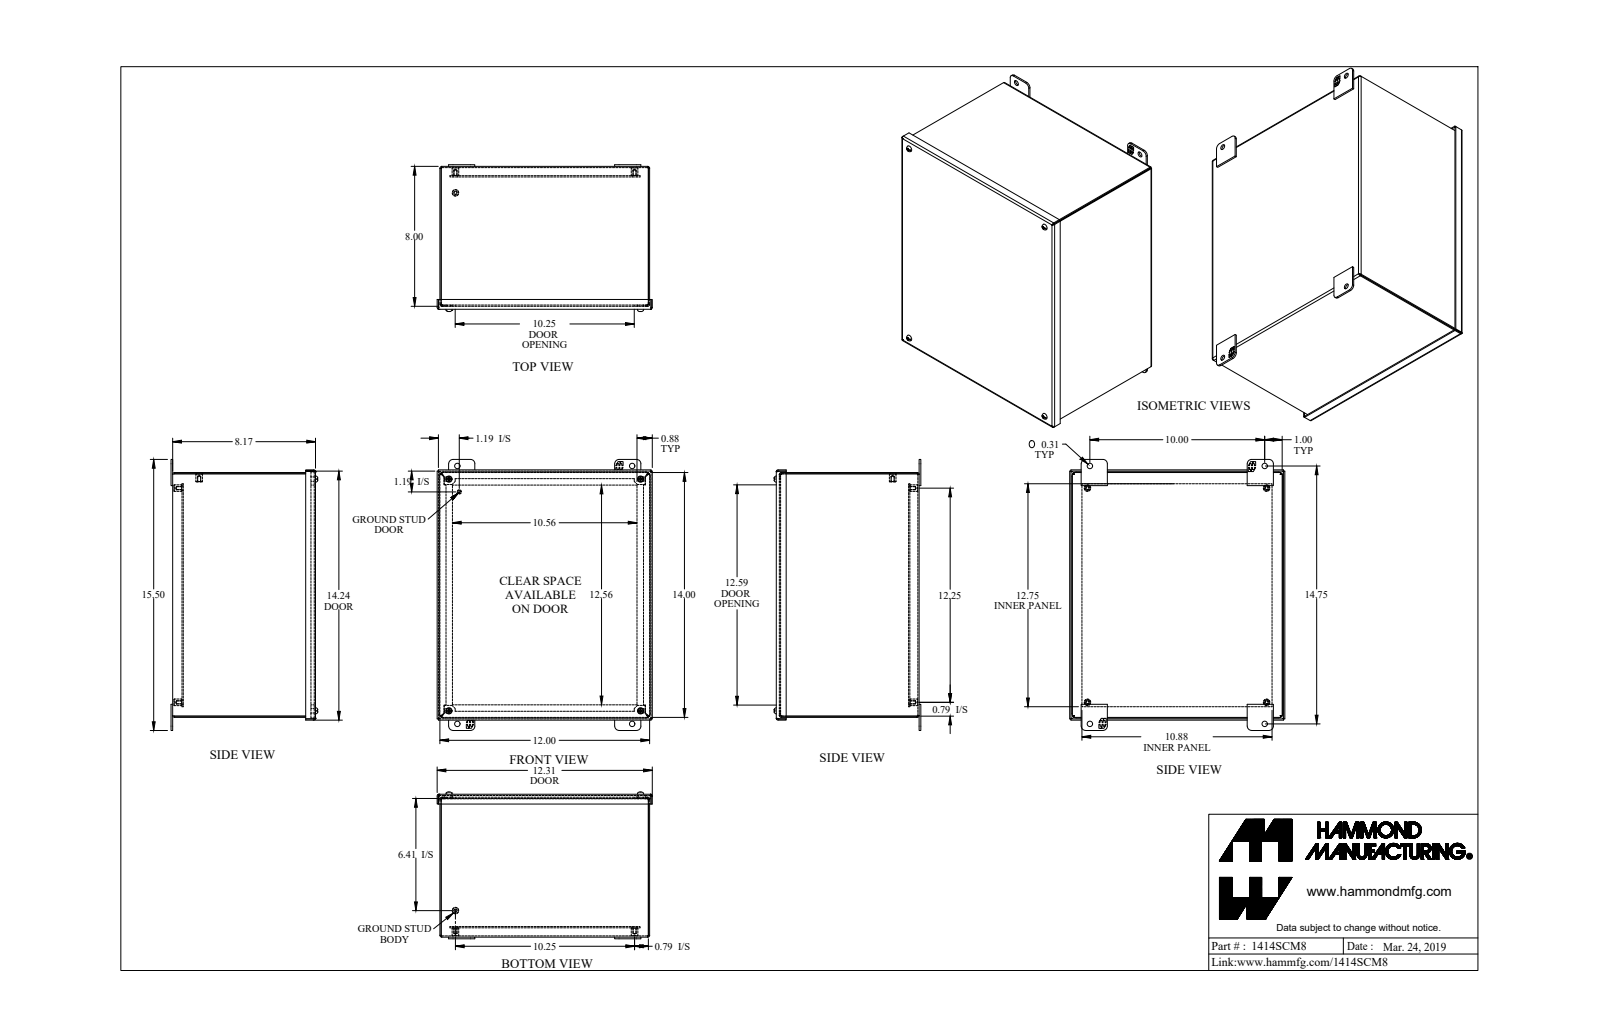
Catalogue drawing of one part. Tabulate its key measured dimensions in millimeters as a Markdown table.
| quantity | value |
| --- | --- |
| part name | 1414SCM8 |
| STEP written by | SolidWorks 2019 (AUTOMOTIVE_DESIGN) |
| units | millimeters |
| bodies | 30 solids, 710 faces (478 planar, 172 cylindrical, 60 other) |
| overall size | 393.7 × 312.7 × 213.2 |
| volume | 1 226 000 mm³ |
| surface area | 1 288 000 mm² |
| round holes (diameter × count) | 4 × 5, 4 × 4, 6.4 × 4, 6.7 × 4, 7.9 × 4 |
| round bosses / shafts (diameter × count) | 9.5 × 5, 9.9 × 4, 7 × 4, 4.8 × 4, 3.8 × 4, 6.4 × 1, 4.8 × 1 |
| partial cylindrical surfaces (radius × count) | 6.4 × 12, 0.2 × 8, 0.9 × 8, 2 × 8, 2.7 × 8, 3.2 × 8, 7.1 × 8, 4.1 × 4 |
| main face-to-face distances | 1.8, 205.7, 192.2, 13.5, 303, 353.8, 207.6, 203.9, 194.1, 11.7 |
| hole center spacings | 266.9, 22.6, 355.8, 444.2, 254, 260.4, 278.3, 278.3 |
